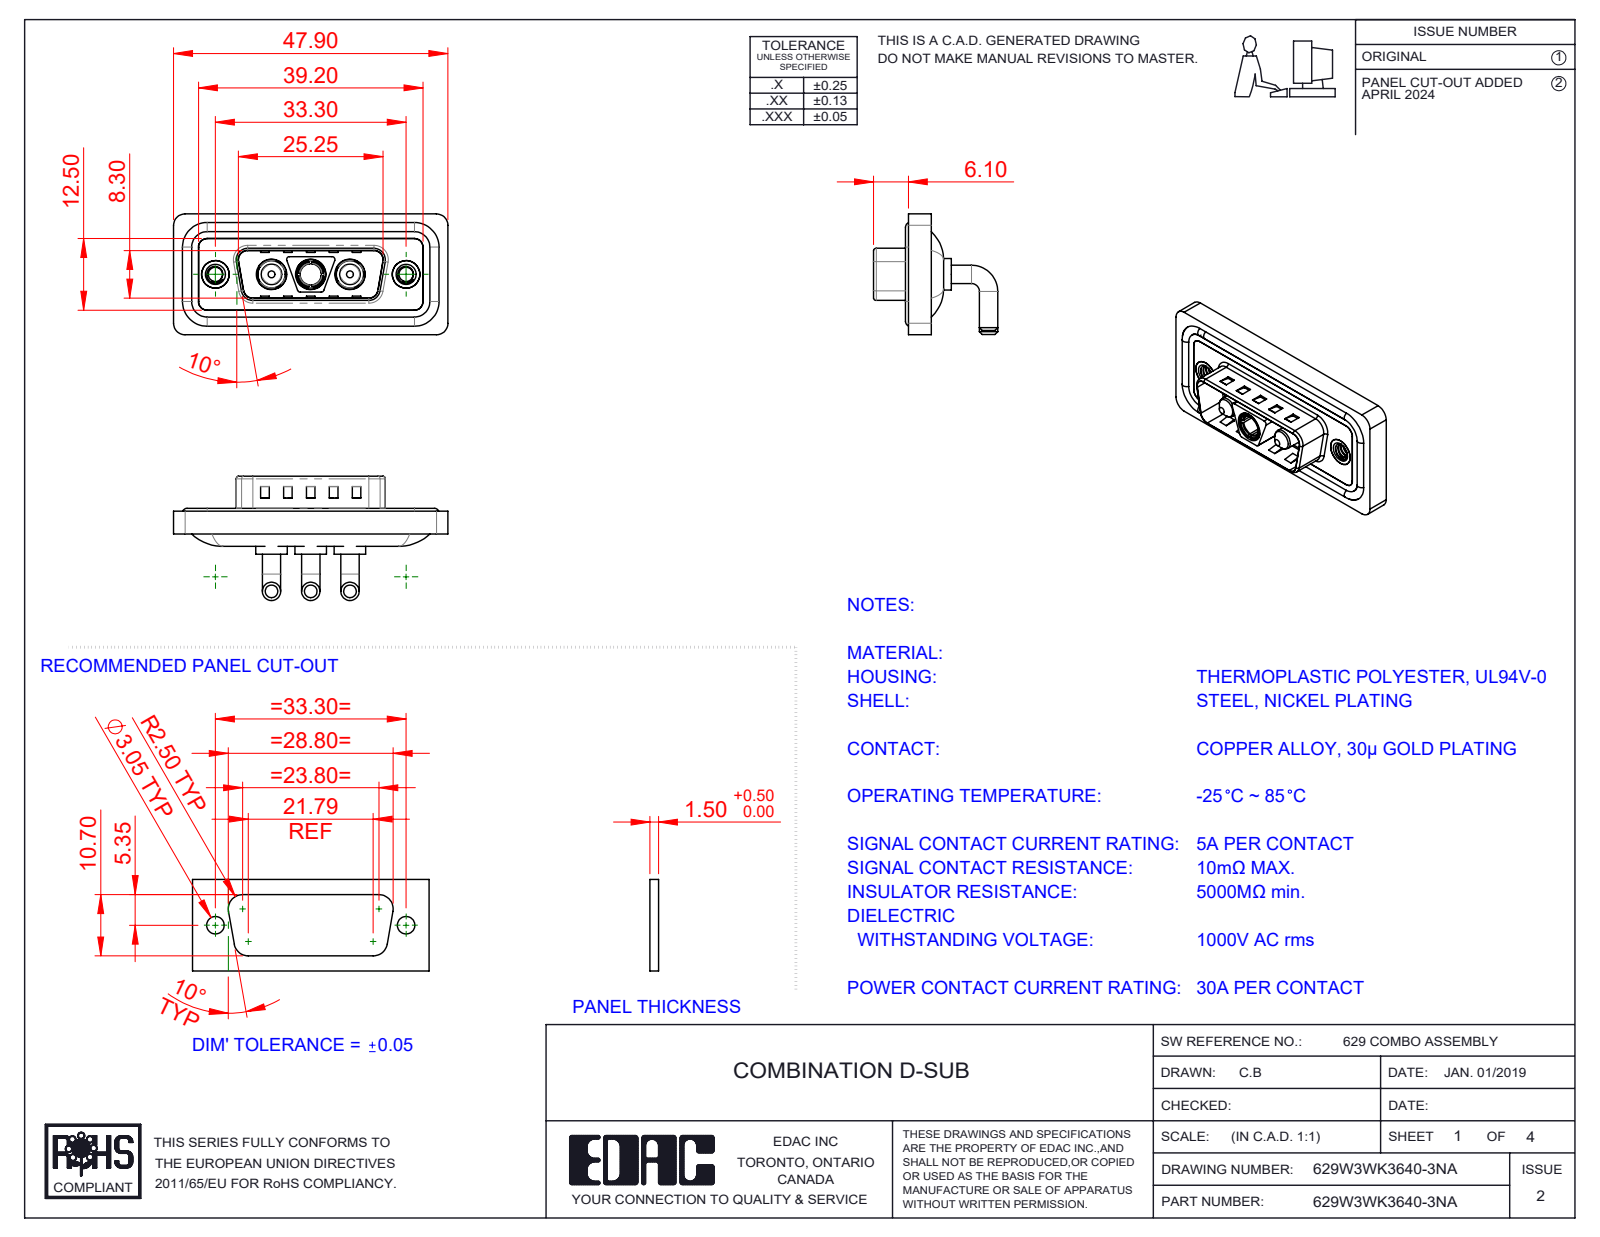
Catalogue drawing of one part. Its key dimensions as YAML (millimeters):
part_name: "629Combo Threaded Rivet_A; 629W3WK3640-3NA; 629Combo Waterproof Housing_15 Contacts; Power Pin_30A RA (+4 more)"
step_written_by: "SolidWorks 2023 (CONFIG_CONTROL_DESIGN)"
units: millimeters
bodies: {solids: 13, faces: 615, planar: 231, cylindrical: 254, other: 130}
overall_size: [47.9, 21.7, 21.1]
volume: 5974
surface_area: 9476
round_holes:
  - {diameter: 4.85, count: 3}
  - {diameter: 5.3, count: 3}
  - {diameter: 2.5, count: 2}
  - {diameter: 4, count: 2}
  - {diameter: 4.8, count: 2}
  - {diameter: 5, count: 2}
  - {diameter: 3.7, count: 1}
round_bosses_or_shafts:
  - {diameter: 3.2, count: 6}
  - {diameter: 1.6, count: 4}
  - {diameter: 5.5, count: 3}
  - {diameter: 5.2, count: 3}
  - {diameter: 4.75, count: 3}
  - {diameter: 3.75, count: 3}
  - {diameter: 4.9, count: 2}
  - {diameter: 3.6, count: 2}
partial_cylinders:
  - {radius: 2, count: 20}
  - {radius: 1.5, count: 18}
  - {radius: 0.5, count: 12}
  - {radius: 1.6, count: 8}
  - {radius: 0.25, count: 4}
  - {radius: 0.6, count: 4}
  - {radius: 0.65, count: 4}
  - {radius: 0.9, count: 4}
face_to_face_distances: [0.4, 2.9, 0.8, 1.1, 2.1, 1.6, 4.5, 3.1, 2.5, 3.7]
hole_center_spacings: [6.85, 9.8, 16.65, 23.5, 13.7, 33.3]
